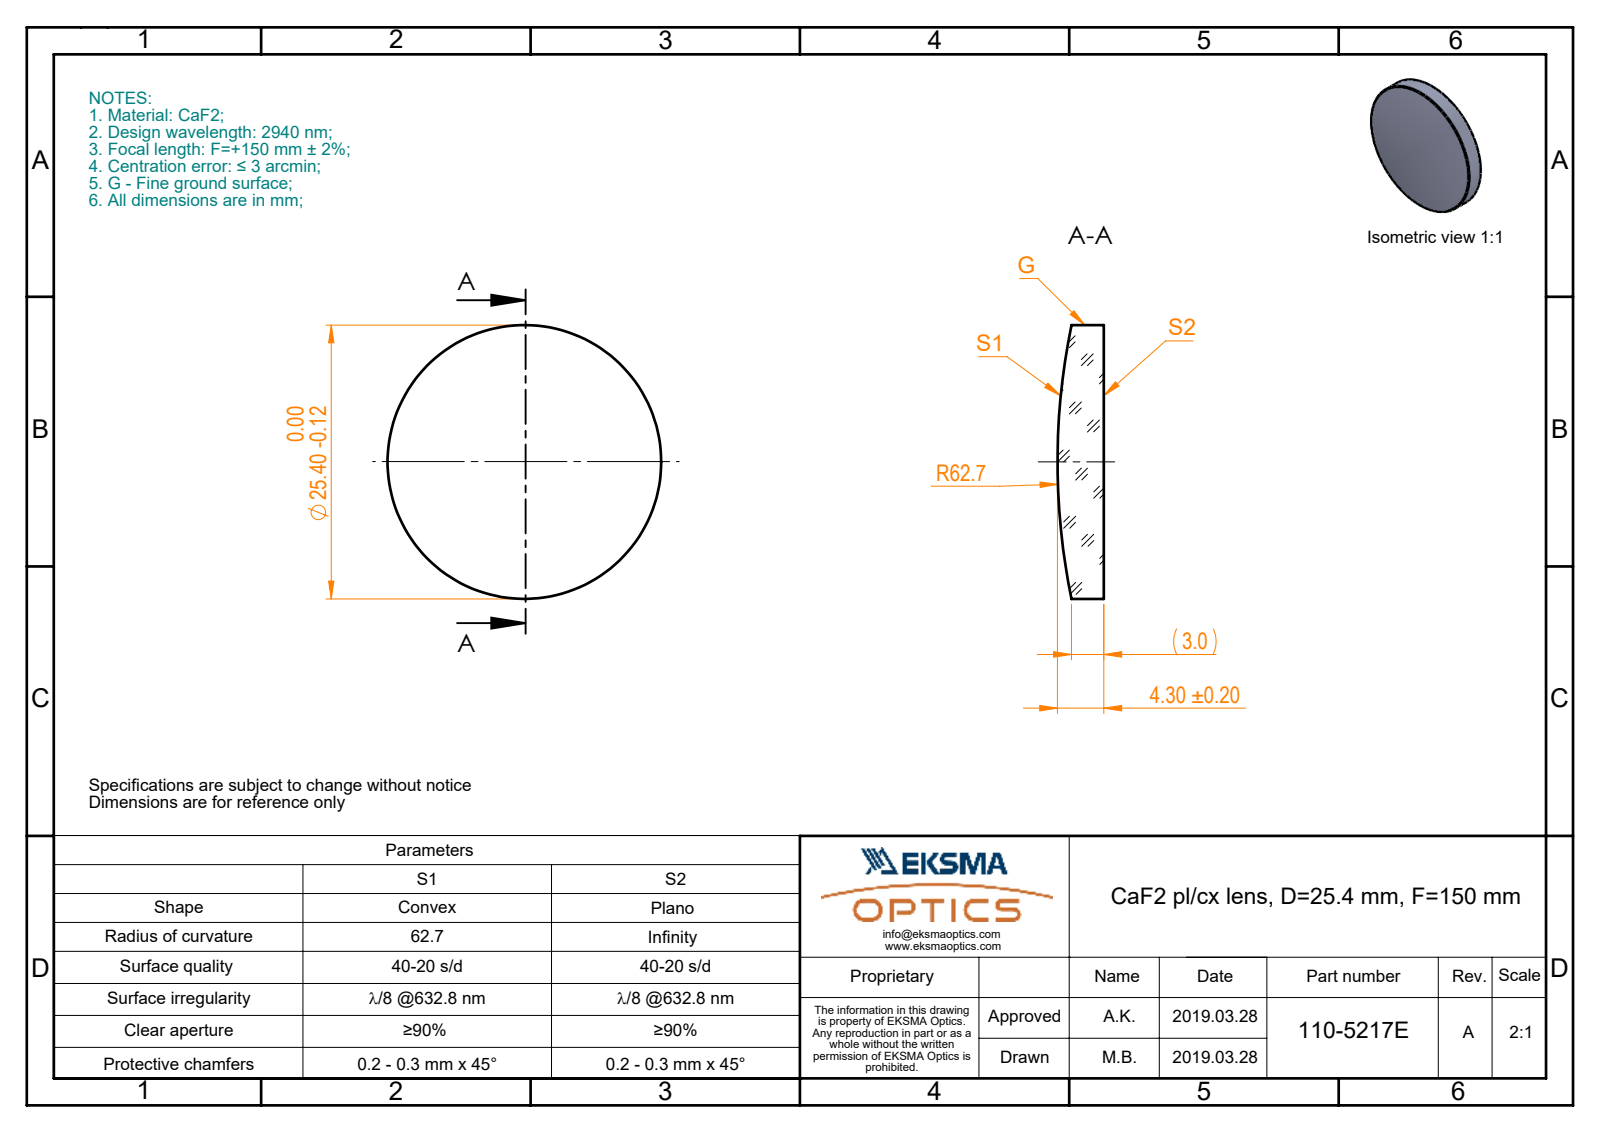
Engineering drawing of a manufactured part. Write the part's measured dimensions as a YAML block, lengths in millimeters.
part_name: "110-5217E CaF2 pl-cx 25.4 F150"
step_written_by: "SolidWorks 2017 (CONFIG_CONTROL_DESIGN)"
units: millimeters
bodies: {solids: 1, faces: 5, planar: 1, cylindrical: 2, other: 2}
overall_size: [25.4, 25.4, 4.3]
volume: 1851
surface_area: 1258
round_bosses_or_shafts:
  - {diameter: 25.4, count: 1}
